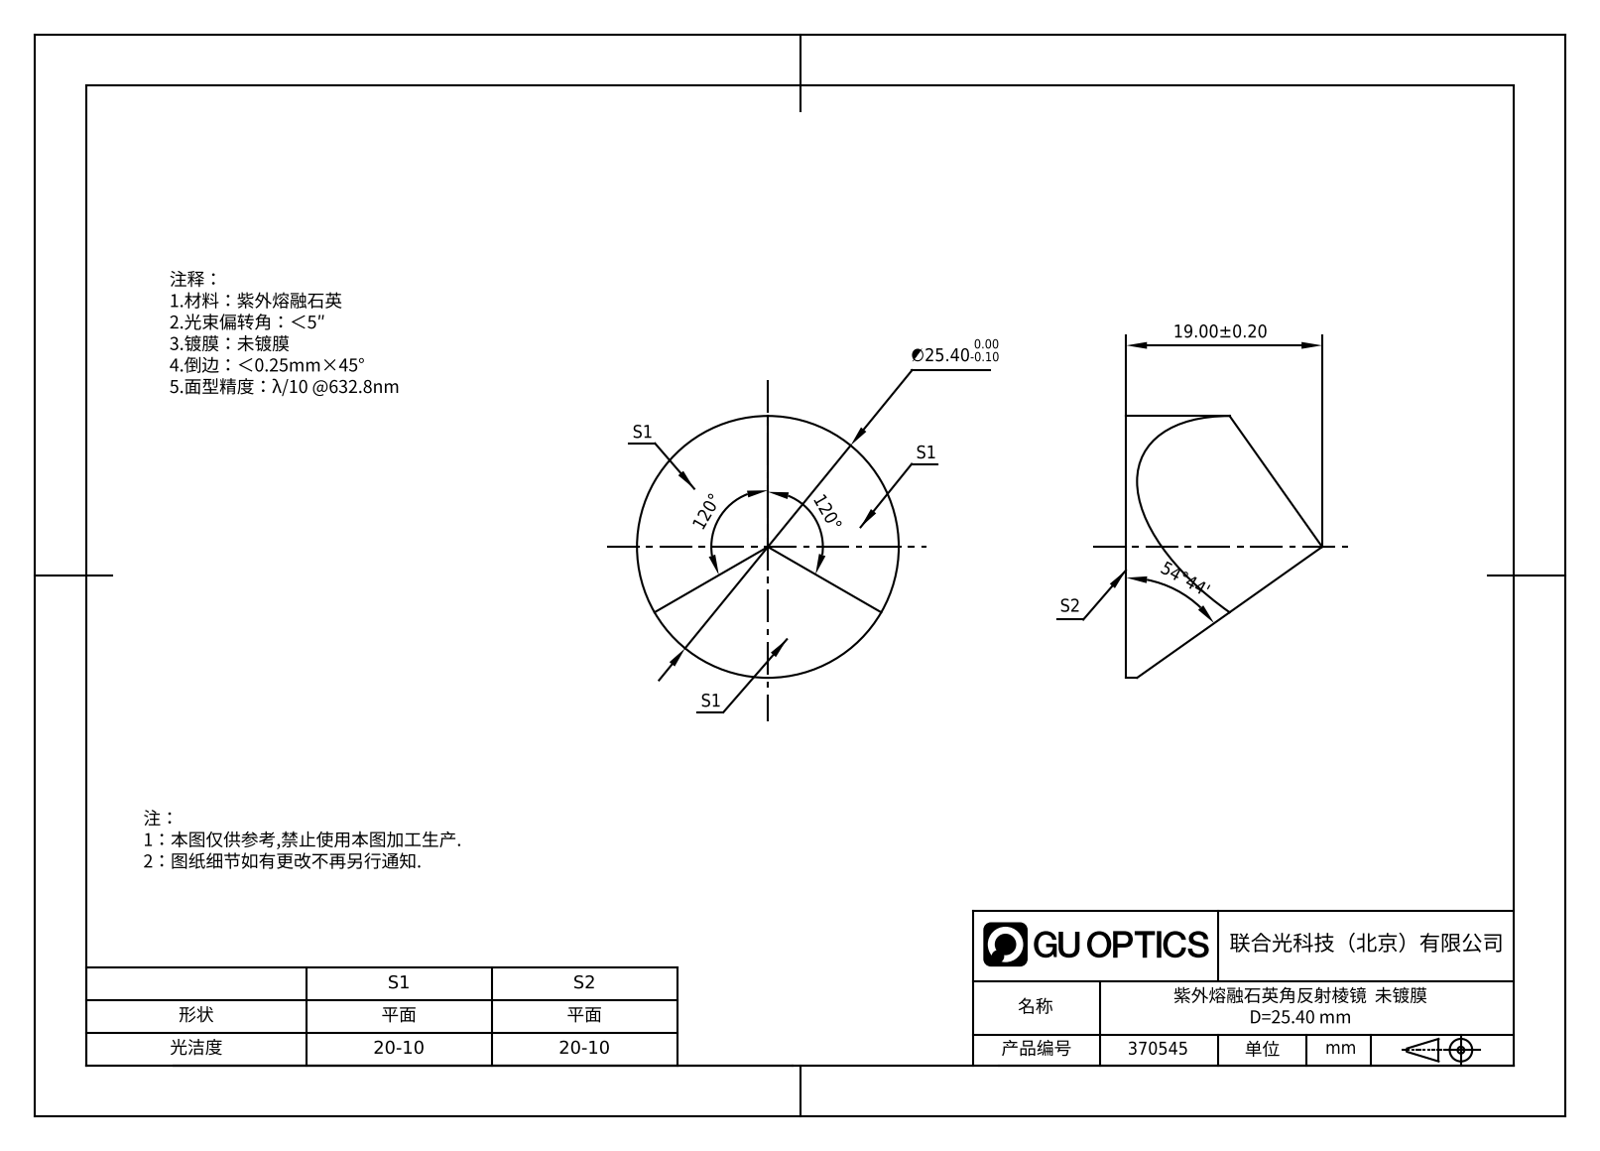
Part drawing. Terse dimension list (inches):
name: GP26-025-3
written by: SolidWorks 2022 (AUTOMOTIVE_DESIGN)
unit: in
bodies: 1 solid, 12 faces (8 planar, 2 cylindrical, 2 other)
size: 1 × 1 × 0.744
volume: 0.281 in³; area: 2.647 in²
bosses: 1× ⌀1
face distances: 0.743
